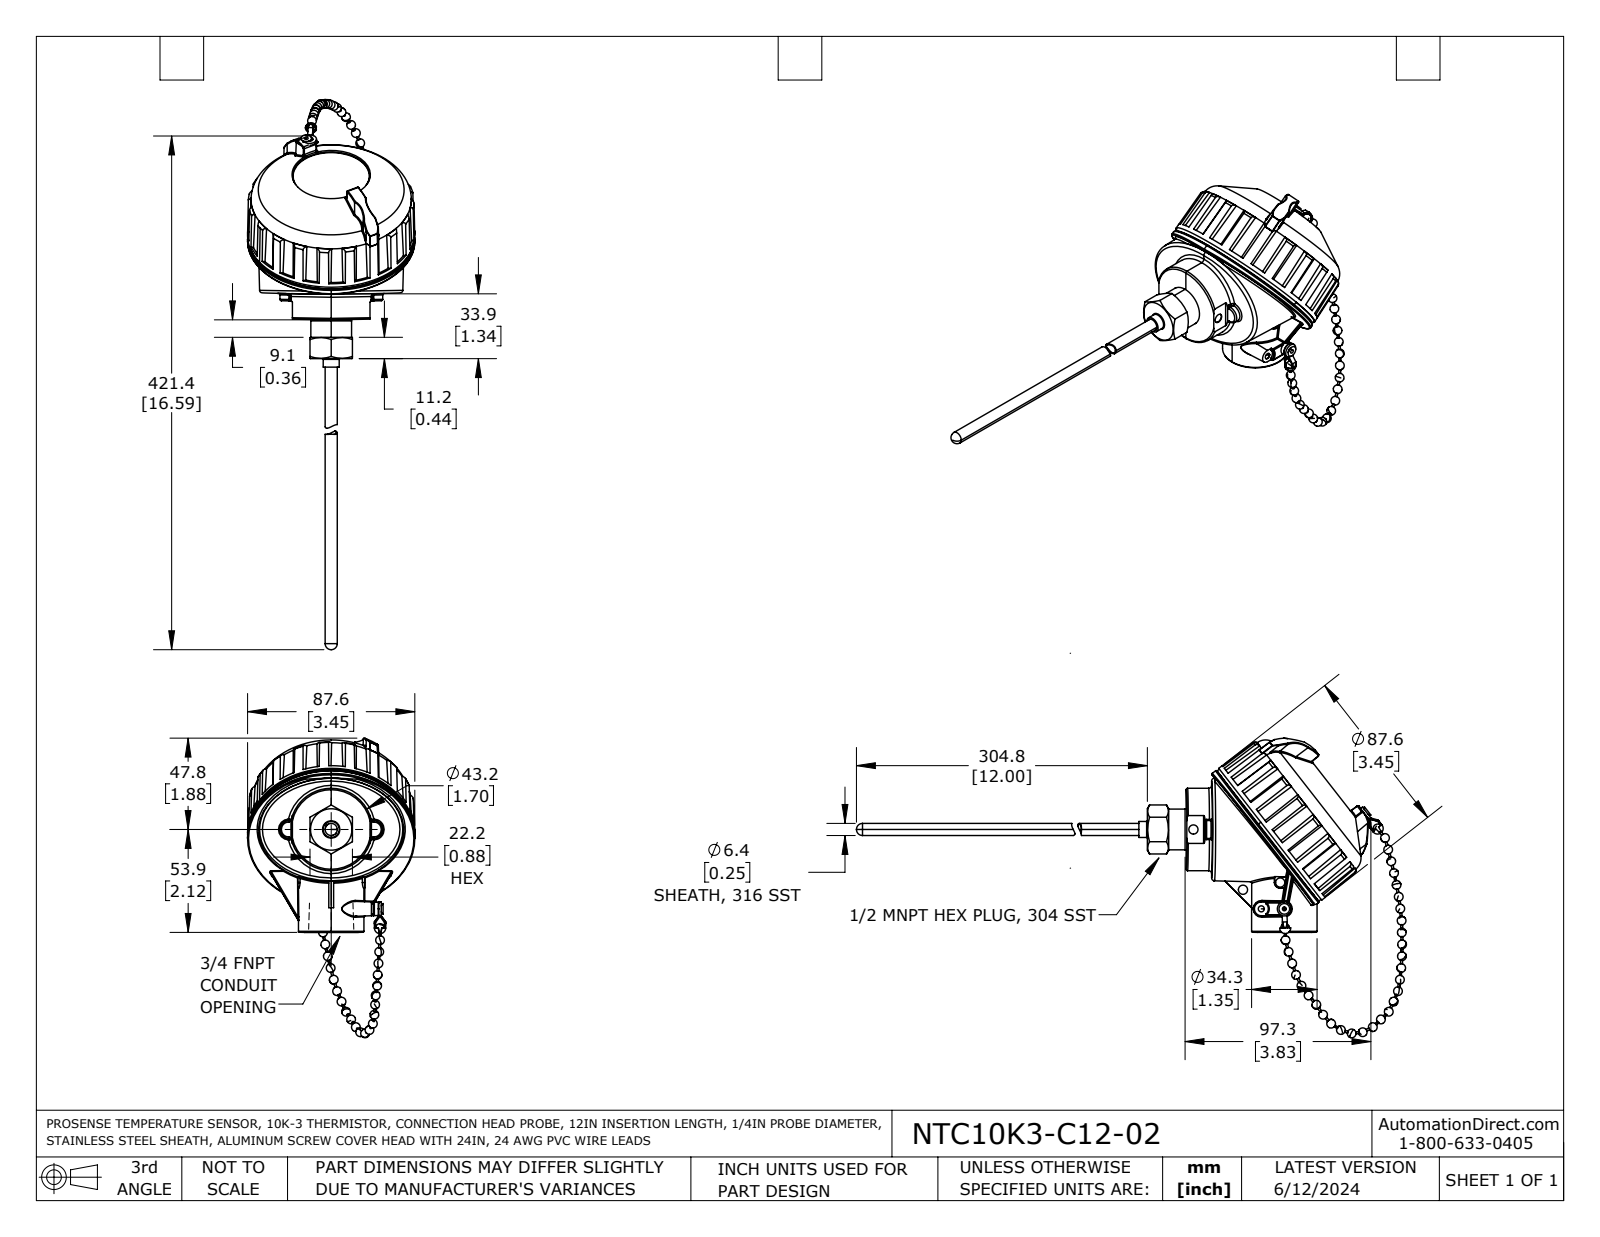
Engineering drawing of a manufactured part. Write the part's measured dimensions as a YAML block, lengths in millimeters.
part_name: "NTC10K3-C12-02"
step_written_by: "SolidWorks 2021 (AUTOMOTIVE_DESIGN)"
units: millimeters
bodies: {solids: 10, faces: 982, planar: 232, cylindrical: 189, other: 561}
overall_size: [440.4, 156.9, 87.6]
volume: 150000
surface_area: 83810
round_holes:
  - {diameter: 4.8, count: 3}
  - {diameter: 2, count: 2}
  - {diameter: 3.7, count: 2}
  - {diameter: 3.2, count: 1}
  - {diameter: 4.2, count: 1}
  - {diameter: 5.3, count: 1}
  - {diameter: 6.4, count: 1}
  - {diameter: 11.1, count: 1}
  - {diameter: 22.6, count: 1}
  - {diameter: 76.3, count: 1}
  - {diameter: 76.9, count: 1}
  - {diameter: 80, count: 1}
round_bosses_or_shafts:
  - {diameter: 1, count: 31}
  - {diameter: 7.4, count: 2}
  - {diameter: 3.1, count: 2}
  - {diameter: 87.6, count: 1}
  - {diameter: 86.5, count: 1}
  - {diameter: 79.3, count: 1}
  - {diameter: 76, count: 1}
  - {diameter: 43.2, count: 1}
partial_cylinders:
  - {radius: 0.5, count: 21}
  - {radius: 0.8, count: 11}
  - {radius: 0.4, count: 6}
  - {radius: 1.5, count: 5}
  - {radius: 4.7, count: 2}
  - {radius: 1.6, count: 1}
  - {radius: 3.7, count: 1}
face_to_face_distances: [37.7, 36.1, 1.6, 3.6, 39.6, 41.2, 13.3, 39.6, 36.1, 1.6]
hole_center_spacings: [1.8, 12.1, 13.9, 13.9, 17, 19.9, 23.9, 25]
